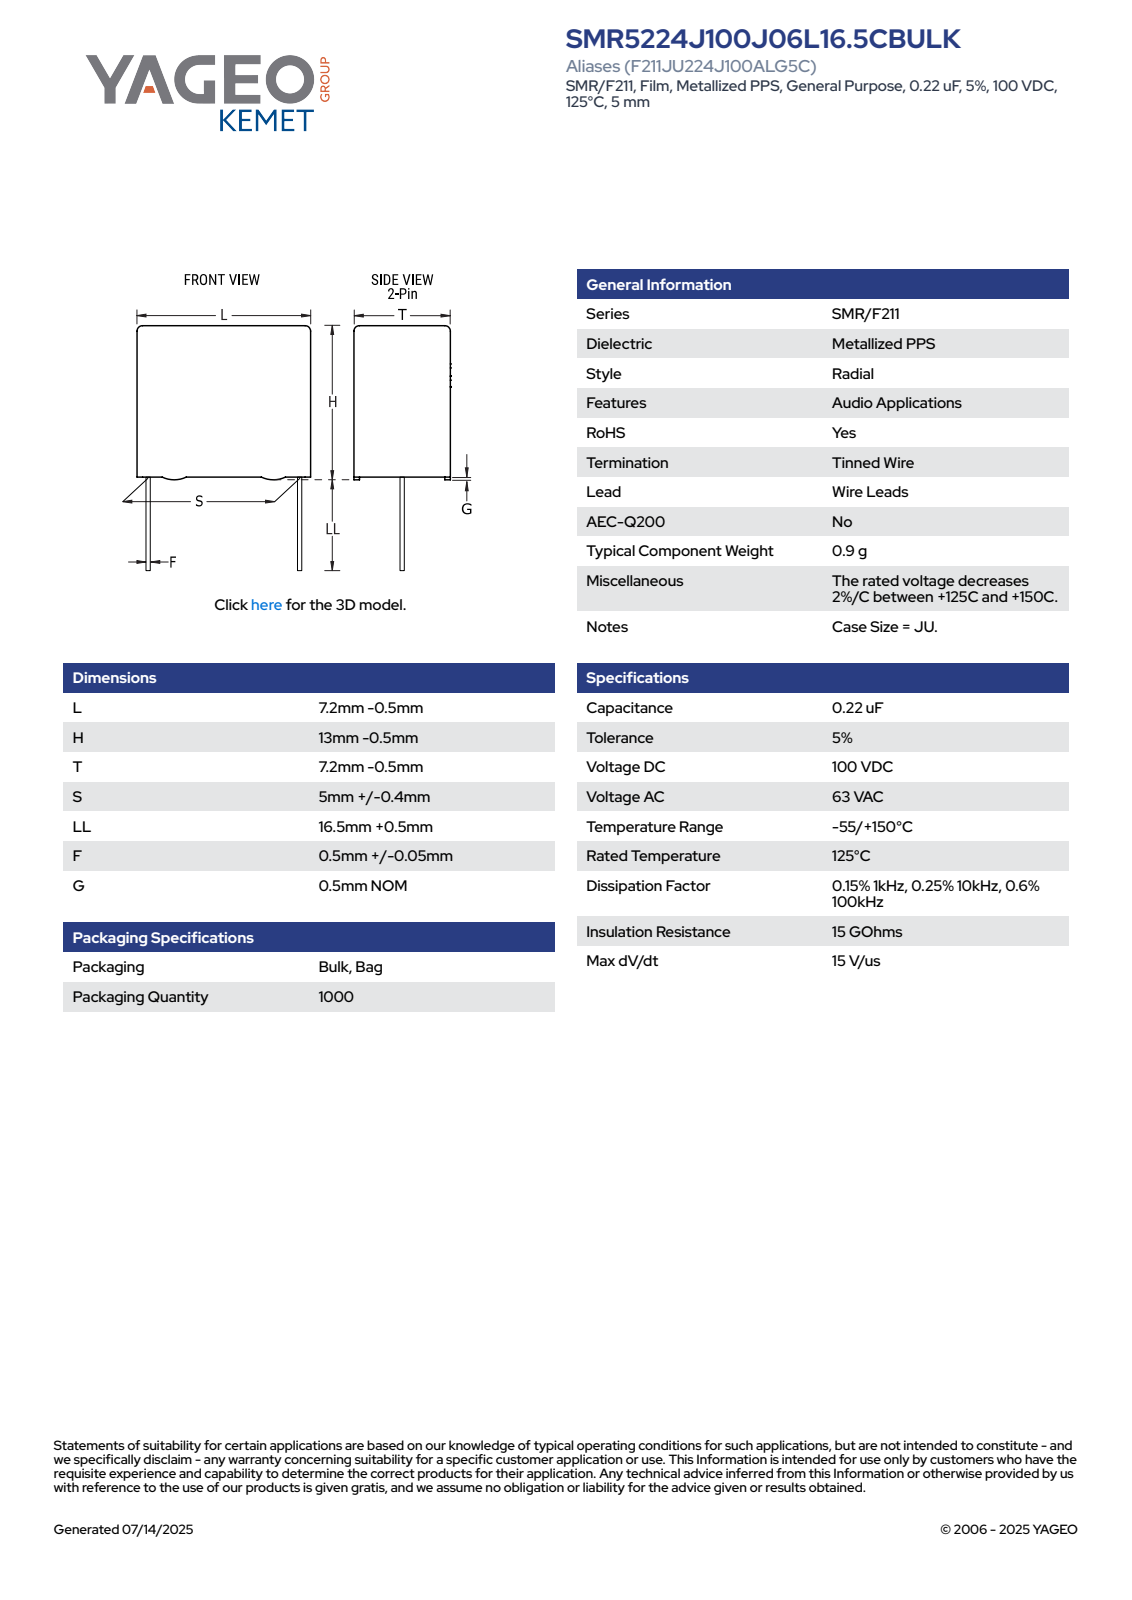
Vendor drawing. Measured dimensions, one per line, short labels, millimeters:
name: CFR_RBG_7.2X13X7.2_L6.7H12.5T6.7S5LL17F0.55G0.5
written by: SolidWorks 2021 (AUTOMOTIVE_DESIGN)
unit: mm
bodies: 4 solids, 89 faces (81 planar, 8 cylindrical, 0 other)
size: 29.5 × 6.71 × 6.7
volume: 547 mm³; area: 477 mm²
bosses: 2× ⌀0.55
rounds: 4× R0.5
face distances: 6.7, 12, 6.32, 0.38, 0.5, 12.5, 6.71, 6.33, 0.39, 5.94
